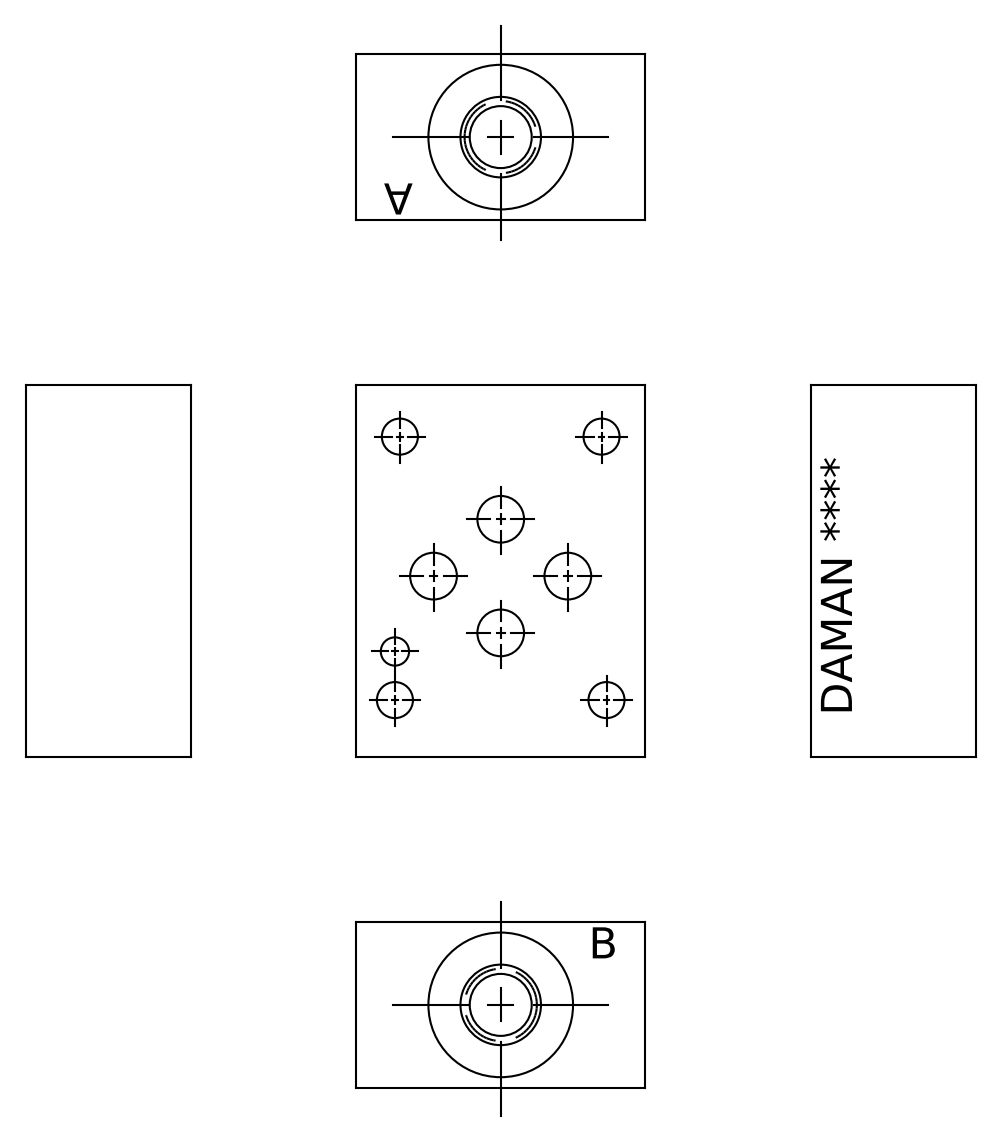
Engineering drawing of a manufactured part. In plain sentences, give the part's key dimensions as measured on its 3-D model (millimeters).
The part is named "Part_AD03TPAB4B.B01854R1_3D". Its 3-D file was written by "Autodesk Inventor 2022 (AUTOMOTIVE_DESIGN)". It is 1 solid with 430 faces: 287 planar, 29 cylindrical and 114 other. Overall it measures 57.15 by 44.45 by 25.4 millimeters. Its volume is 55 191 cubic millimeters and its surface area 14 060 square millimeters. Round holes: 8 of diameter 7.14, 4 of diameter 5.54, 4 of diameter 12.7, 1 of diameter 3.17, 1 of diameter 3.96, 1 of diameter 11.1, 1 of diameter 11.68, 1 of diameter 13.26, 1 of diameter 22.12. Partial cylindrical surfaces (rounded edges, fillets, slot ends): 3 of radius 2.77. The main face-to-face distances are 25.4, 44.45, 57.15, 0.79, 56.36, 24.08, 1.32, 55.57, 44.41, 12.57. The hole center spacings are 13.52, 13.53, 16.5, 20.65, 28.99, 13, 13.54, 17.48.
